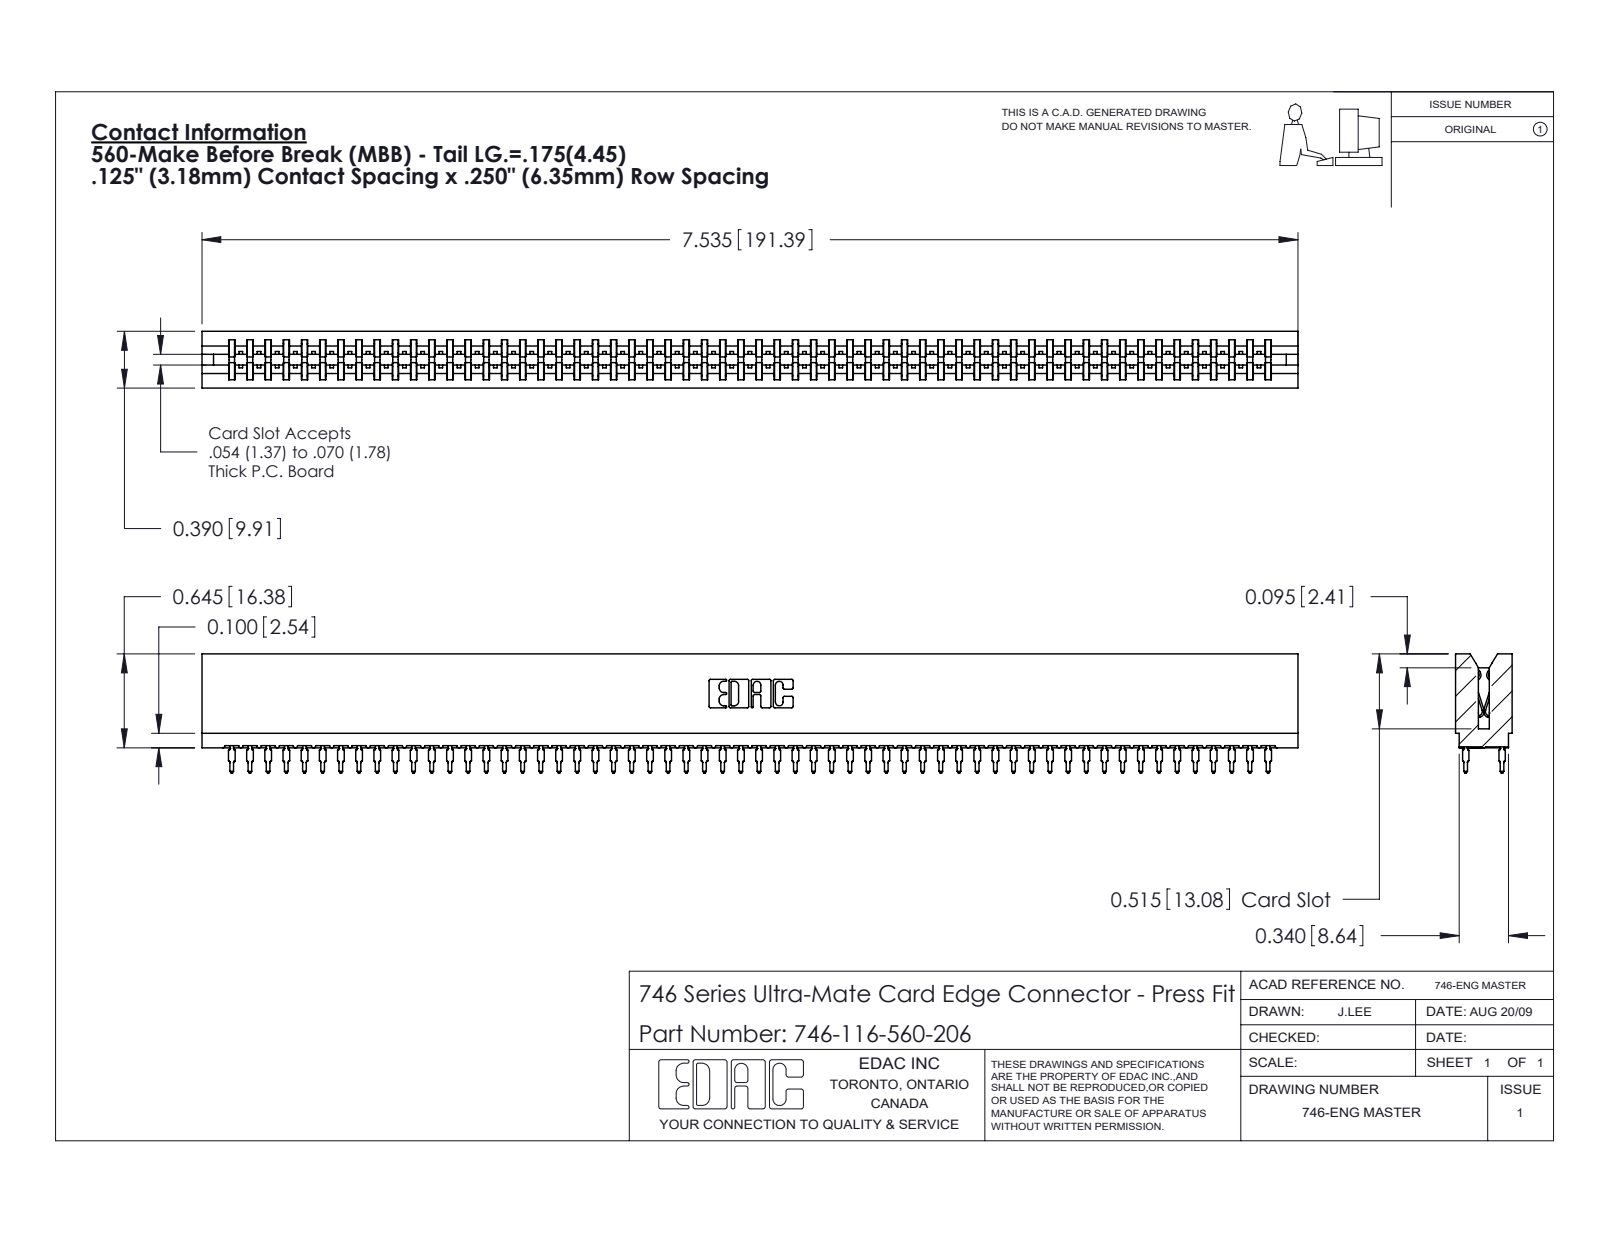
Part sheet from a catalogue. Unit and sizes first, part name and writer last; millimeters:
Units: millimetres
Overall size (bounding box): 191.4 × 20.8 × 9.9
Partial cylindrical surfaces — rounded edges, fillets, slot ends (radius × count): R0.5 ×232, R0.4 ×59, R0.3 ×22, R0.1 ×8, R0.3 ×8, R0.2 ×6, R0.8 ×6, R0.5 ×4
Main face-to-face distances: 1.4, 8.5, 9.9, 6.4, 0.6, 7.8, 7, 2.1, 0.3, 4.4
Volume: 20 830 mm³ · Surface area: 35 970 mm²
Bodies: 117 solids, 11060 faces (5508 planar, 2536 cylindrical, 3016 other)
Part name (STEP PRODUCT): 746-292-001_560; 746-116-560-206; 746 Part_.515 Slot Depth - 06
STEP written by: SolidWorks 2020 (CONFIG_CONTROL_DESIGN)
